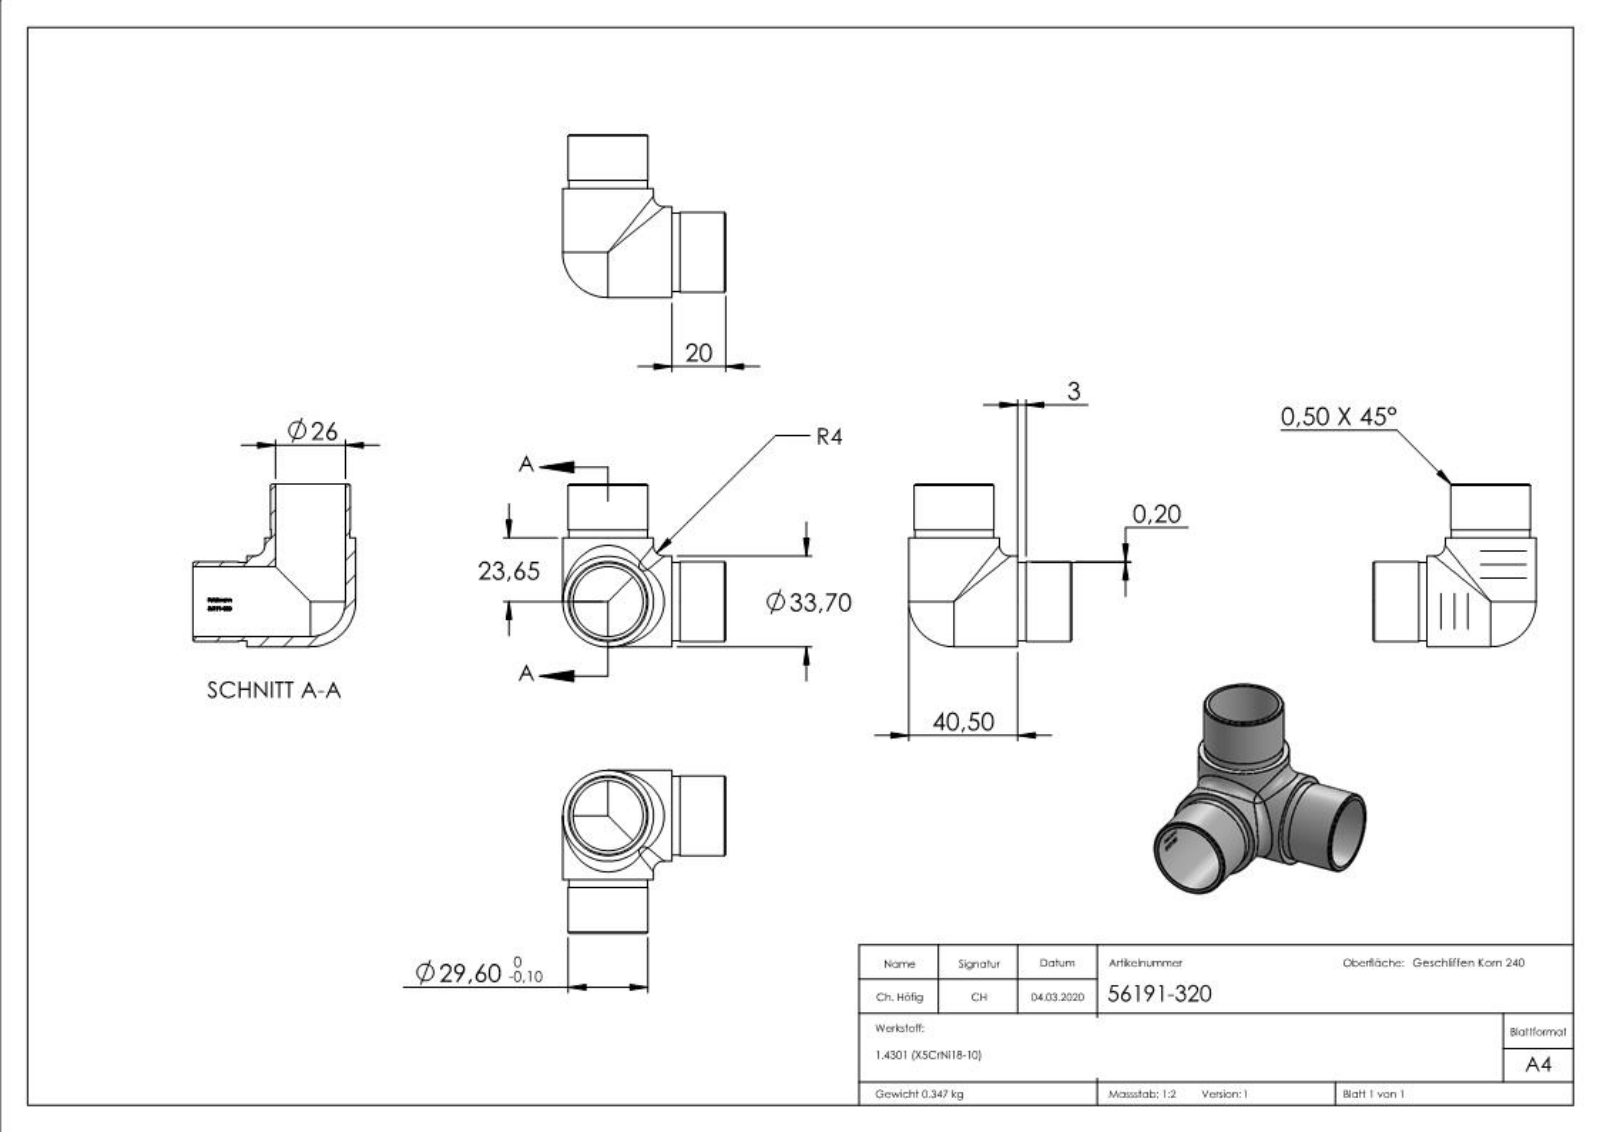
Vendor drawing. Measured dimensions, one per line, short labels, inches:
name: 56191-320
written by: SolidWorks 2015 (CONFIG_CONTROL_DESIGN)
unit: in
bodies: 1 solid, 30 faces (9 planar, 12 cylindrical, 9 other)
size: 2.382 × 2.382 × 2.382
volume: 1.683 in³; area: 32.35 in²
holes: 3× ⌀1.024
bosses: 3× ⌀1.327, 3× ⌀1.165, 3× ⌀1.15
face distances: 0.787, 0.118, 0.669
